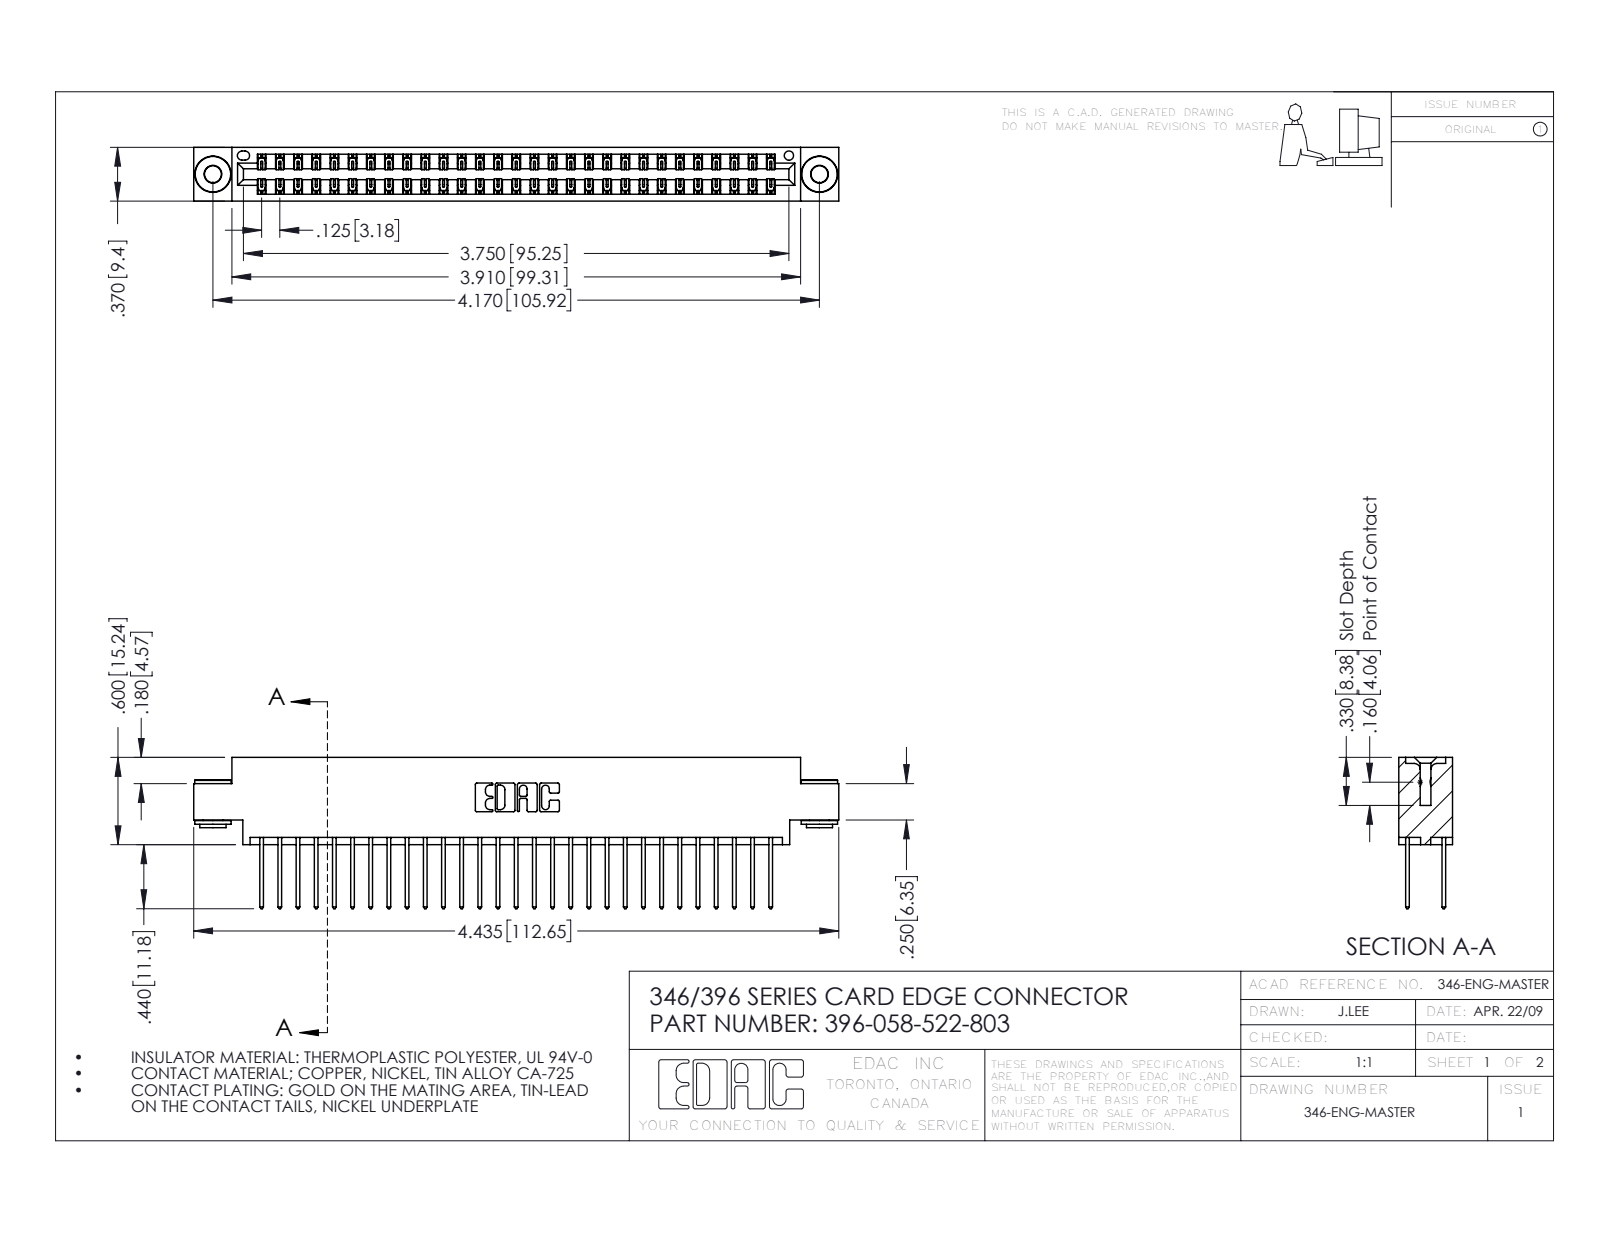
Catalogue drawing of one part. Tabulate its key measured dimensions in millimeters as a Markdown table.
| quantity | value |
| --- | --- |
| part name | 345-250-002_345-250-002-102; 345-292-001_345-293-122; 346 Part_0.170 Offset - 0.156 Dia-TH; 396-058-522-803 |
| STEP written by | SolidWorks 2016 (CONFIG_CONTROL_DESIGN) |
| units | millimeters |
| bodies | 61 solids, 3180 faces (2120 planar, 1052 cylindrical, 8 other) |
| overall size | 112.6 × 26.4 × 9.4 |
| volume | 10 900 mm³ |
| surface area | 15 860 mm² |
| round holes (diameter × count) | 2.9 × 2, 4 × 2, 1.6 × 1 |
| round bosses / shafts (diameter × count) | 6.4 × 2, 4.6 × 2, 3.5 × 2 |
| partial cylindrical surfaces (radius × count) | 0.2 × 87, 0.3 × 58, 0.3 × 22, 0.2 × 6, 0.8 × 6, 0.7 × 3, 0.4 × 2, 0.6 × 2 |
| main face-to-face distances | 1.2, 8.2, 6.4, 9.4, 0.6, 1.8, 7.6, 7, 3.8, 5.6 |
| hole center spacings | 6.2, 100.6, 105.9 |
